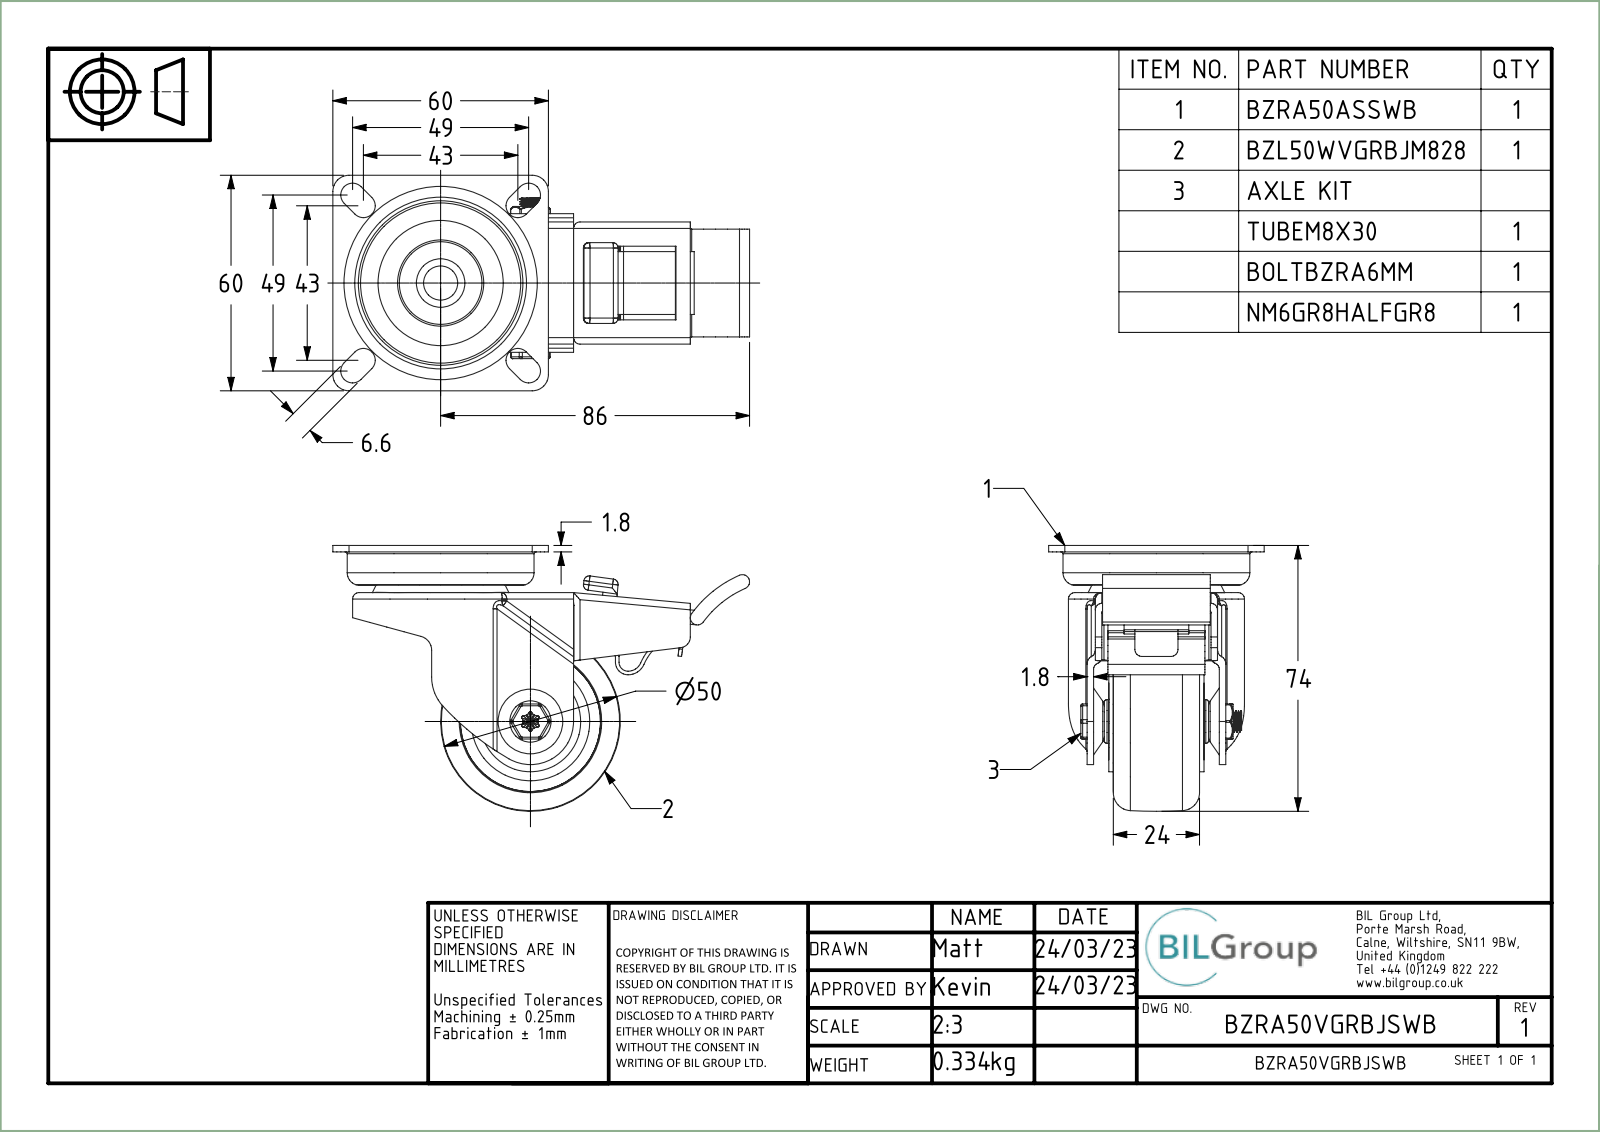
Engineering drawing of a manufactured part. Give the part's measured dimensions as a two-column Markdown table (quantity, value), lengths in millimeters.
| quantity | value |
| --- | --- |
| part name | BZRA50ASSWB; BRAKE PAD; ZINC PLATED PRESSED STEEL TOP PLATE; ZINC PLATED PRESSED STEEL FORKS (+8 more) |
| STEP written by | Spatial InterOp 3D (CONFIG_CONTROL_DESIGN) |
| units | millimeters |
| bodies | 32 solids, 833 faces (232 planar, 362 cylindrical, 239 other) |
| overall size | 116 × 74 × 60 |
| volume | 76 926 mm³ |
| surface area | 67 226 mm² |
| round holes (diameter × count) | 6 × 1, 6.2 × 1, 6.3 × 1, 8.1 × 1, 8.2 × 1, 9.5 × 1, 12.5 × 1, 19.2 × 1, 20 × 1, 20.5 × 1, 22 × 1, 33 × 1 |
| round bosses / shafts (diameter × count) | 52 × 1, 39 × 1, 38 × 1, 28 × 1, 15 × 1, 13.5 × 1, 12.2 × 1, 8 × 1 |
| partial cylindrical surfaces (radius × count) | 1 × 28, 1.8 × 22, 0.5 × 12, 0.9 × 12, 1.5 × 11, 3.3 × 8, 0.4 × 6, 2 × 6 |
| main face-to-face distances | 1.8, 13.12, 1.81, 5, 11.32, 14.92, 14.93, 32.2, 30.4, 29 |
